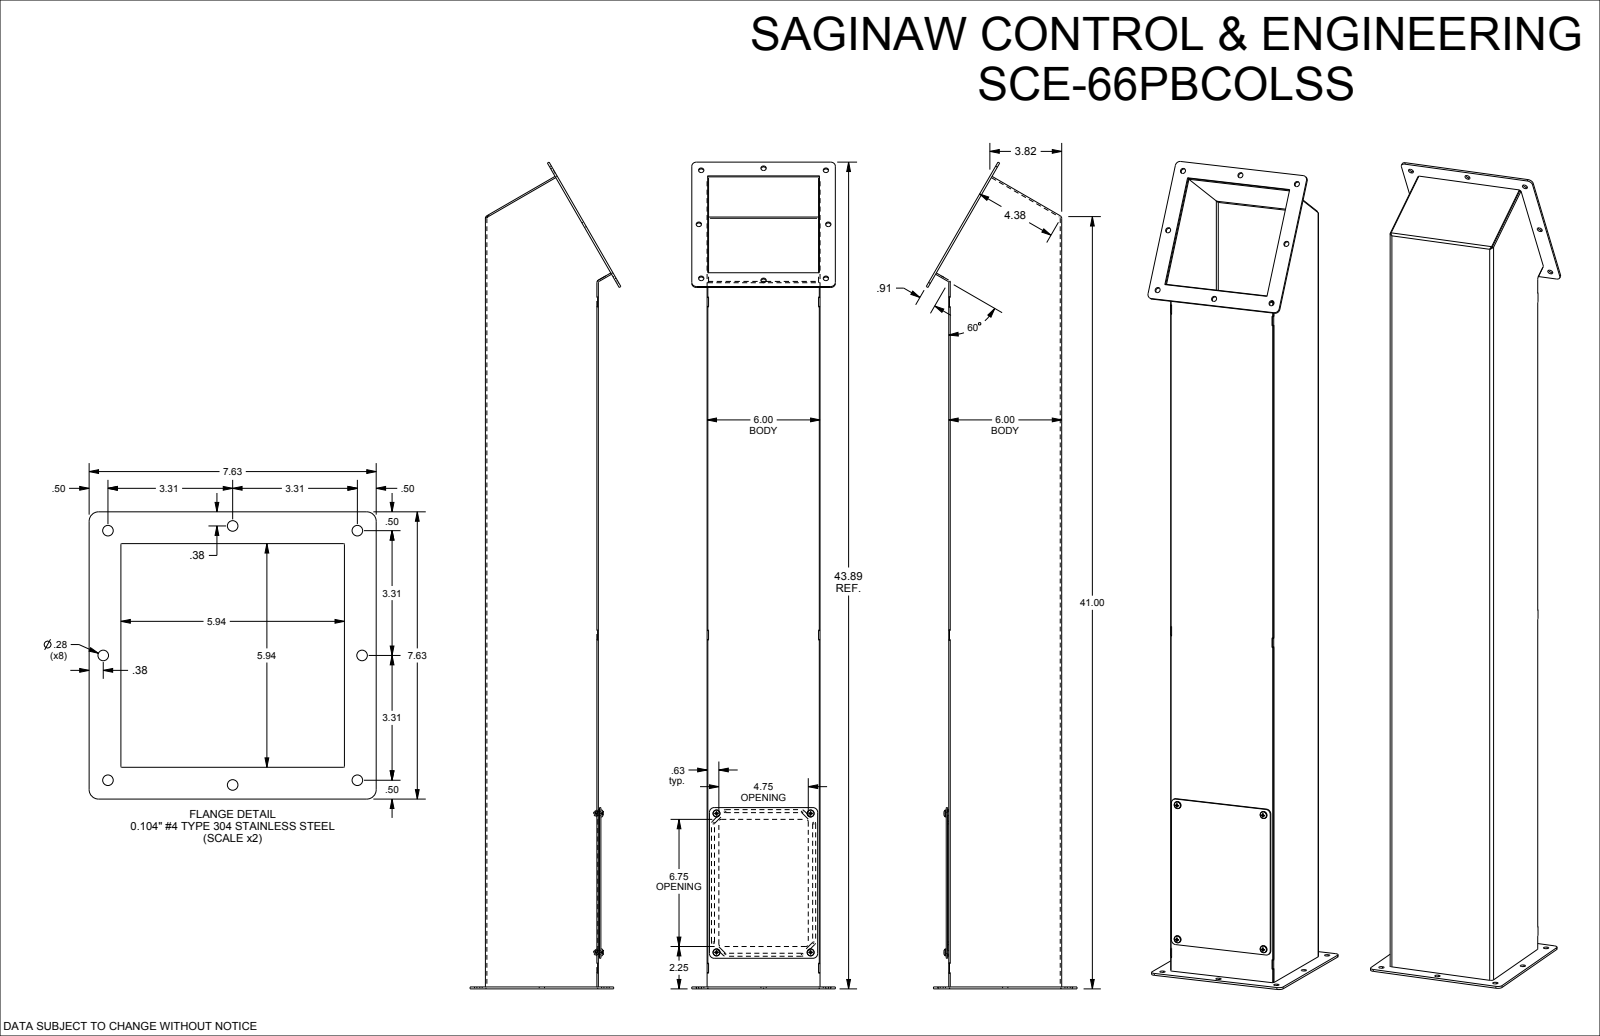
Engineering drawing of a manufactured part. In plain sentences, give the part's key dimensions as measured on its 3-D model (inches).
The part is named "SCE-66PBCOL". Its 3-D file was written by "SolidWorks 2019 (AUTOMOTIVE_DESIGN)". It is 14 solids with 497 faces: 213 planar, 160 cylindrical and 124 other. Overall it measures 43.891 by 8.008 by 7.625 inches. Its volume is 69.61 cubic inches and its surface area 2 124 square inches. Round holes: 8 of diameter 0.281, 4 of diameter 0.19, 4 of diameter 0.218, 4 of diameter 0.25. Round bosses or shafts: 4 of diameter 0.373, 4 of diameter 0.34, 4 of diameter 0.249, 4 of diameter 0.188. Partial cylindrical surfaces (rounded edges, fillets, slot ends): 28 of radius 0.015, 16 of radius 0.01, 16 of radius 0.141, 12 of radius 0.25, 9 of radius 0.08, 8 of radius 0.045, 8 of radius 0.205, 6 of radius 0.063. The main face-to-face distances are 0.06, 5.94, 6, 5.88, 0.078, 5.922, 5.862, 6.06, 0.138, 6.135. The hole center spacings are 6.625, 9.369, 5, 7.375, 8.91.
